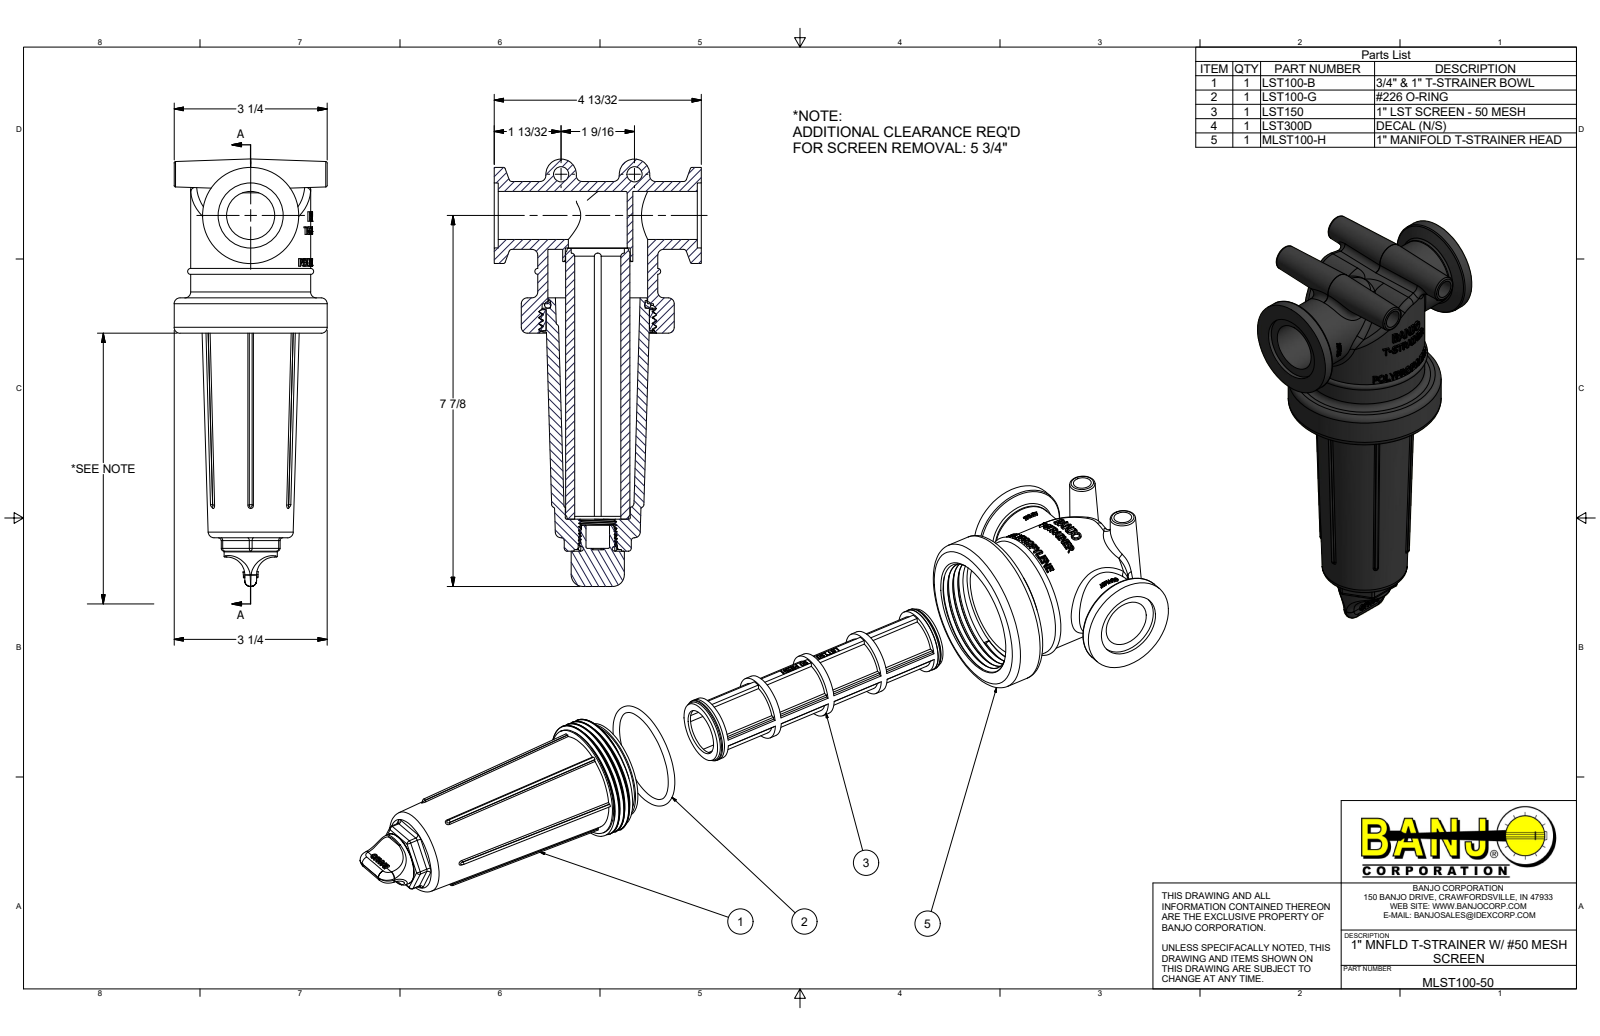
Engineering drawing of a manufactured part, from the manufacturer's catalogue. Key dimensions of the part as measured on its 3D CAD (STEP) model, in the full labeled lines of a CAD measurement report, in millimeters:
Part name (STEP PRODUCT): MLST100-50; MLST100-H; LST100-B; LST100-XB (+4 more)
STEP written by: Autodesk Inventor 2012 (AUTOMOTIVE_DESIGN)
Units: millimetres
Bodies: 7 solids, 1340 faces (692 planar, 160 cylindrical, 488 other)
Overall size (bounding box): 230.6 × 111.8 × 82.6
Volume: 310 400 mm³ · Surface area: 163 000 mm²
Round holes (diameter × count): ⌀35.1 ×2, ⌀12.7 ×1, ⌀24.9 ×1, ⌀25.5 ×1, ⌀25.9 ×1, ⌀27.9 ×1, ⌀31.8 ×1, ⌀53.8 ×1, ⌀55.8 ×1, ⌀60.1 ×1
Round bosses / shafts (diameter × count): ⌀82.6 ×1, ⌀64.8 ×1, ⌀63.5 ×1, ⌀59.4 ×1, ⌀53.3 ×1, ⌀51.8 ×1, ⌀51.1 ×1, ⌀37.8 ×1
Partial cylindrical surfaces — rounded edges, fillets, slot ends (radius × count): R1.5 ×19, R0.8 ×9, R1.9 ×4, R9.7 ×2, R12.7 ×1, R19.1 ×1, R33.4 ×1
Main face-to-face distances: 1.3, 34.3, 6.4, 0.8, 12.2, 19.1, 30.5, 3.8, 38.1, 54
